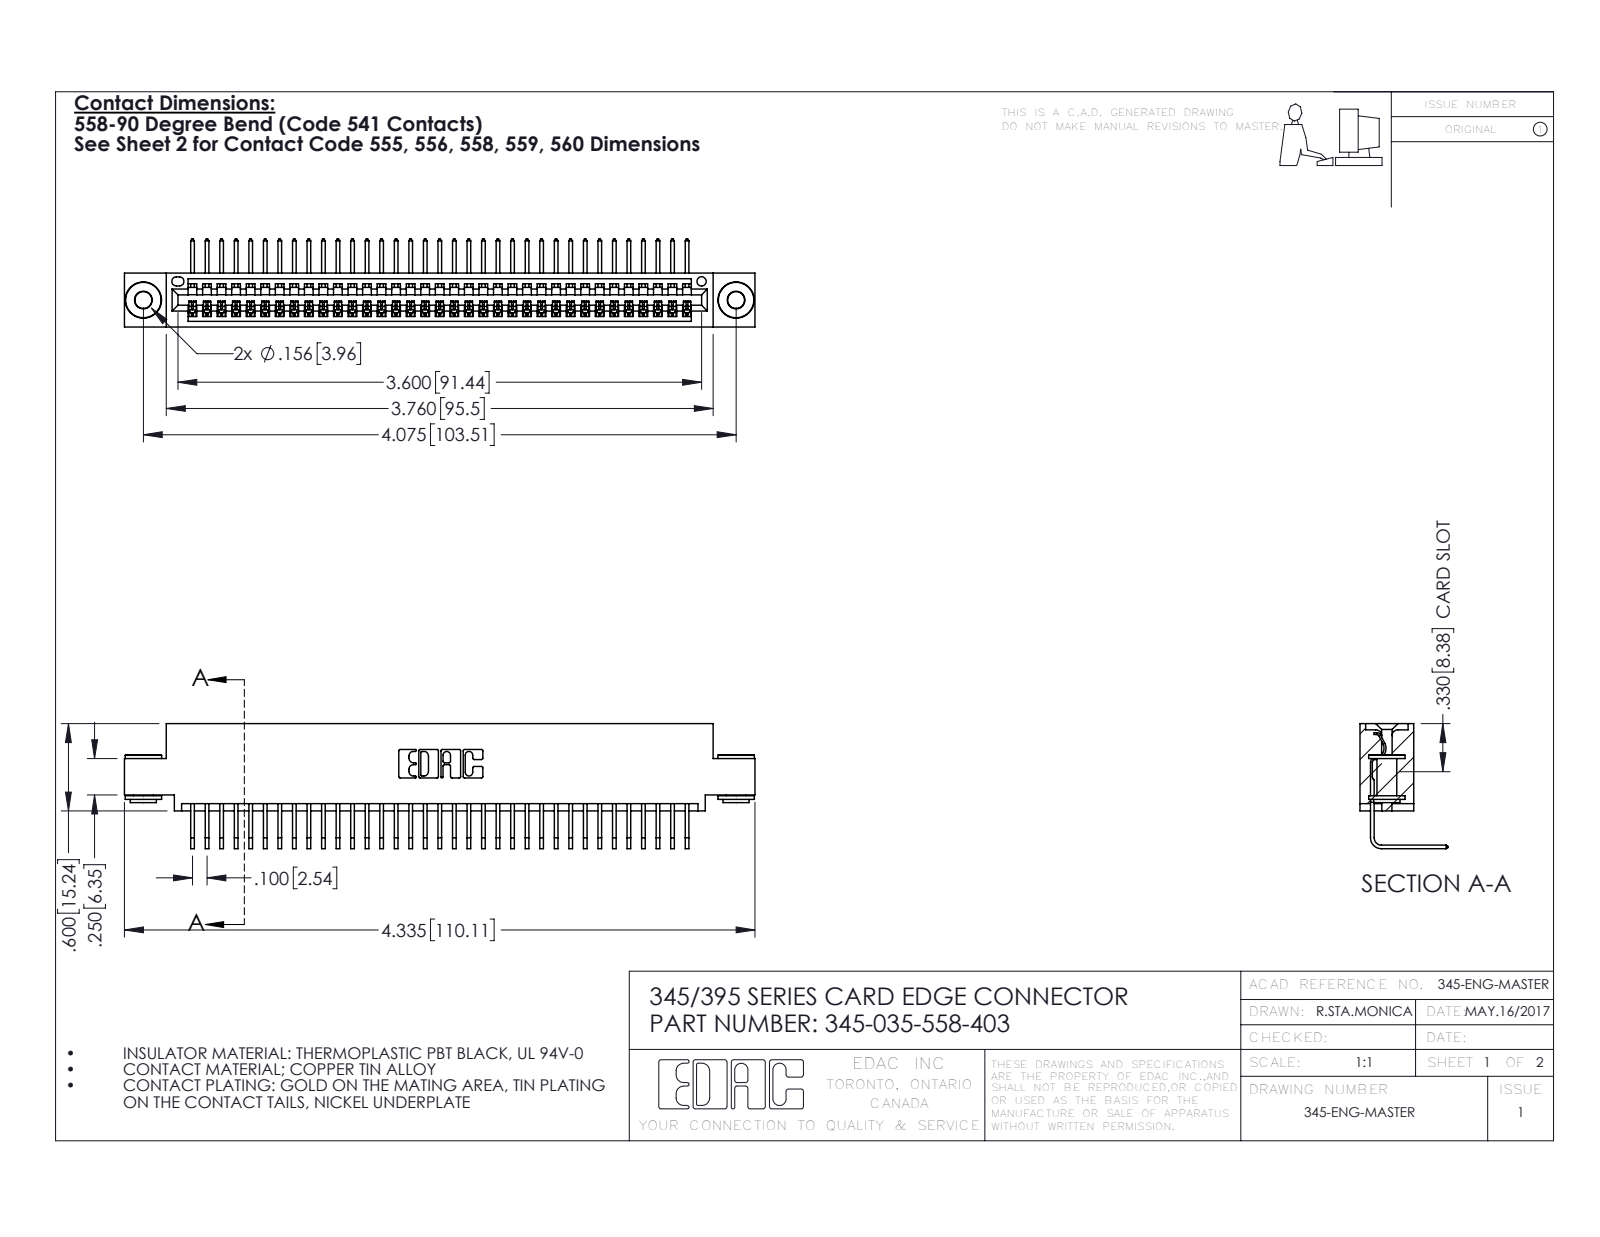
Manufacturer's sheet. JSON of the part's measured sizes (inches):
{"part_name": "345-250-002_345-250-002-102; 345-292-001_558 Tail - 2; 345 Part_0.110 Offset - 0.156 Dia-TH; 345-035-558-403", "step_written_by": "SolidWorks 2016 (CONFIG_CONTROL_DESIGN)", "units": "inches", "bodies": {"solids": 38, "faces": 2268, "planar": 1564, "cylindrical": 696, "other": 8}, "overall_size": [4.335, 0.859, 0.605], "volume_in3": 0.639, "surface_area_in2": 22.93, "round_holes": [[0.116, 2], [0.156, 2], [0.064, 1]], "round_bosses_or_shafts": [[0.25, 2], [0.18, 2], [0.136, 2]], "partial_cylinders_radius": [[0.006, 70], [0.01, 22], [0.007, 6], [0.031, 6], [0.026, 3], [0.031, 2], [0.04, 2], [0.014, 1]], "face_to_face_distances": [0.072, 0.298, 0.37, 0.2, 0.025, 0.098, 0.272, 0.225, 0.149, 0.072], "hole_center_spacings": [0.27, 3.839, 4.075]}
